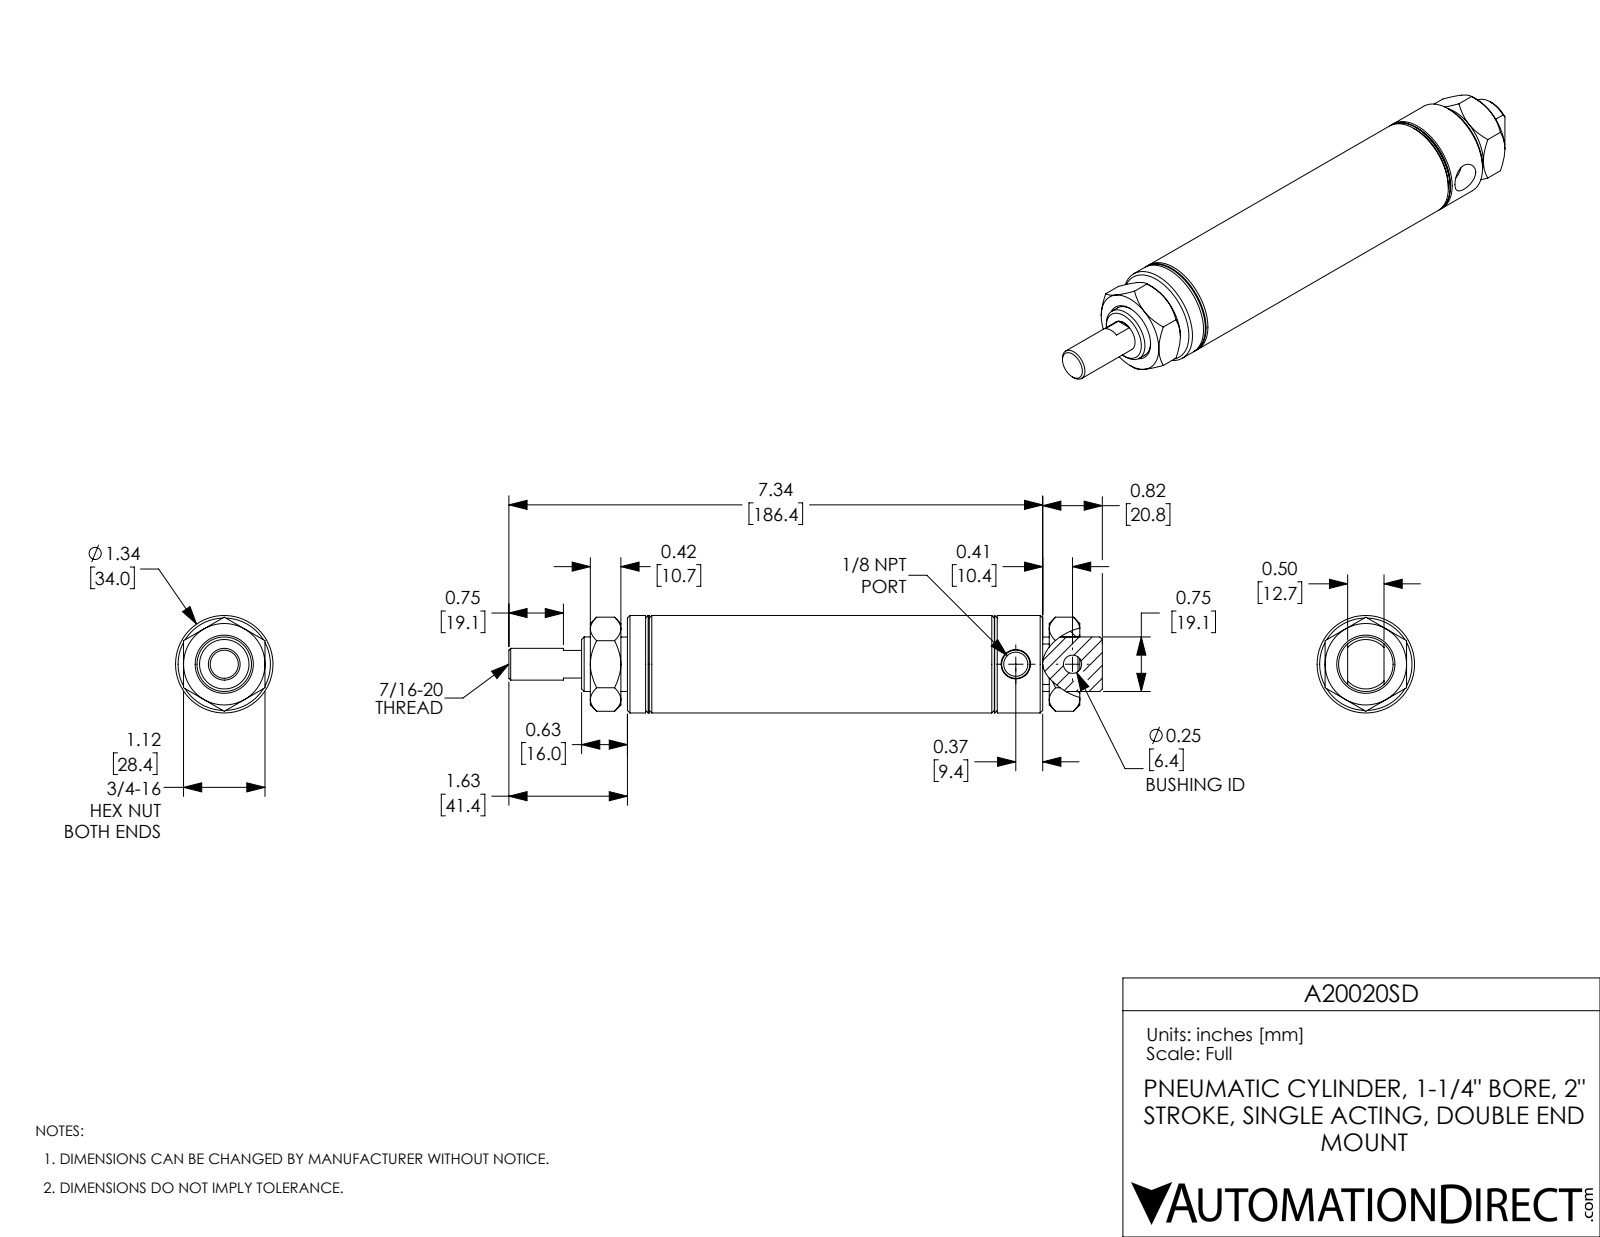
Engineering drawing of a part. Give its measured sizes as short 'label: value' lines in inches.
name: A20020SD-MainBody; A20020SD-Rod; A20020SD; A20020SD_Mounting Nut_D-3556
written by: SolidWorks 2017 (AUTOMOTIVE_DESIGN)
unit: in
bodies: 4 solids, 129 faces (41 planar, 34 cylindrical, 54 other)
size: 8.16 × 1.34 × 1.34
volume: 7.041 in³; area: 65.55 in²
holes: 1× ⌀0.251, 1× ⌀0.332, 1× ⌀0.437, 1× ⌀0.75, 1× ⌀1.25
bosses: 1× ⌀1.34, 1× ⌀0.747
face distances: 1.605, 4.105, 0.5, 1.12, 0.31, 2.5, 2, 0.09, 1.695, 4.195
hole spacings: 0.78
